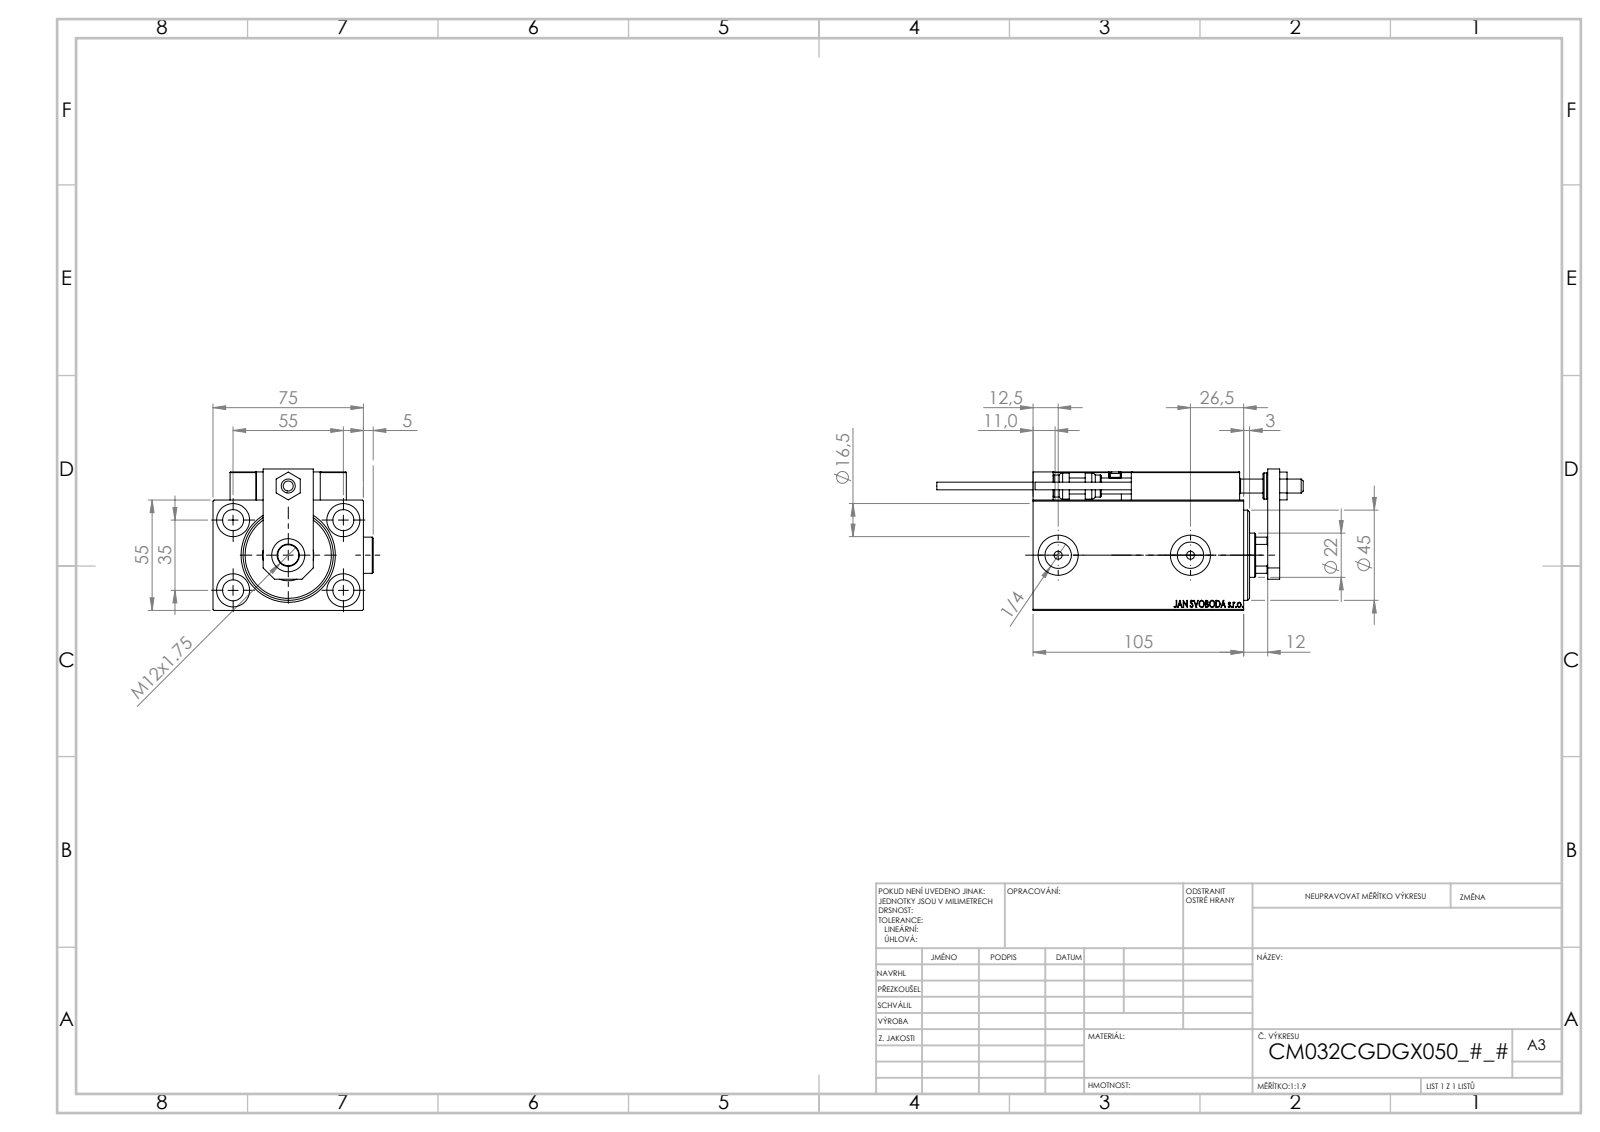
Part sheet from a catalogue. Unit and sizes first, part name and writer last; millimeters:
Units: millimetres
Overall size (bounding box): 182.7 × 79.9 × 70.5
Round holes (diameter × count): ⌀4 ×6, ⌀8 ×5, ⌀10.5 ×5, ⌀16.5 ×5, ⌀3.2 ×4, ⌀5 ×2, ⌀13.16 ×2, ⌀20 ×2, ⌀7 ×1, ⌀22 ×1, ⌀25.5 ×1, ⌀32 ×1
Round bosses / shafts (diameter × count): ⌀18 ×2, ⌀5 ×2, ⌀3.8 ×2, ⌀13 ×1, ⌀11 ×1
Partial cylindrical surfaces — rounded edges, fillets, slot ends (radius × count): R0.3 ×30, R3 ×2, R10.5 ×1
Main face-to-face distances: 55, 75, 14, 10, 12, 5, 69, 7, 15, 25
Hole centre spacings: 32.6, 11.37, 20, 29.59, 29.69, 32.33, 35, 36.06
Volume: 413 825 mm³ · Surface area: 104 987 mm²
Bodies: 25 solids, 1336 faces (594 planar, 204 cylindrical, 538 other)
Part name (STEP PRODUCT): SWITCH DIM B,W; V450CM_C_Body; SWITCH X; Zatka_OIL_PORT (+7 more)
STEP written by: SolidWorks 2019 (CONFIG_CONTROL_DESIGN)
